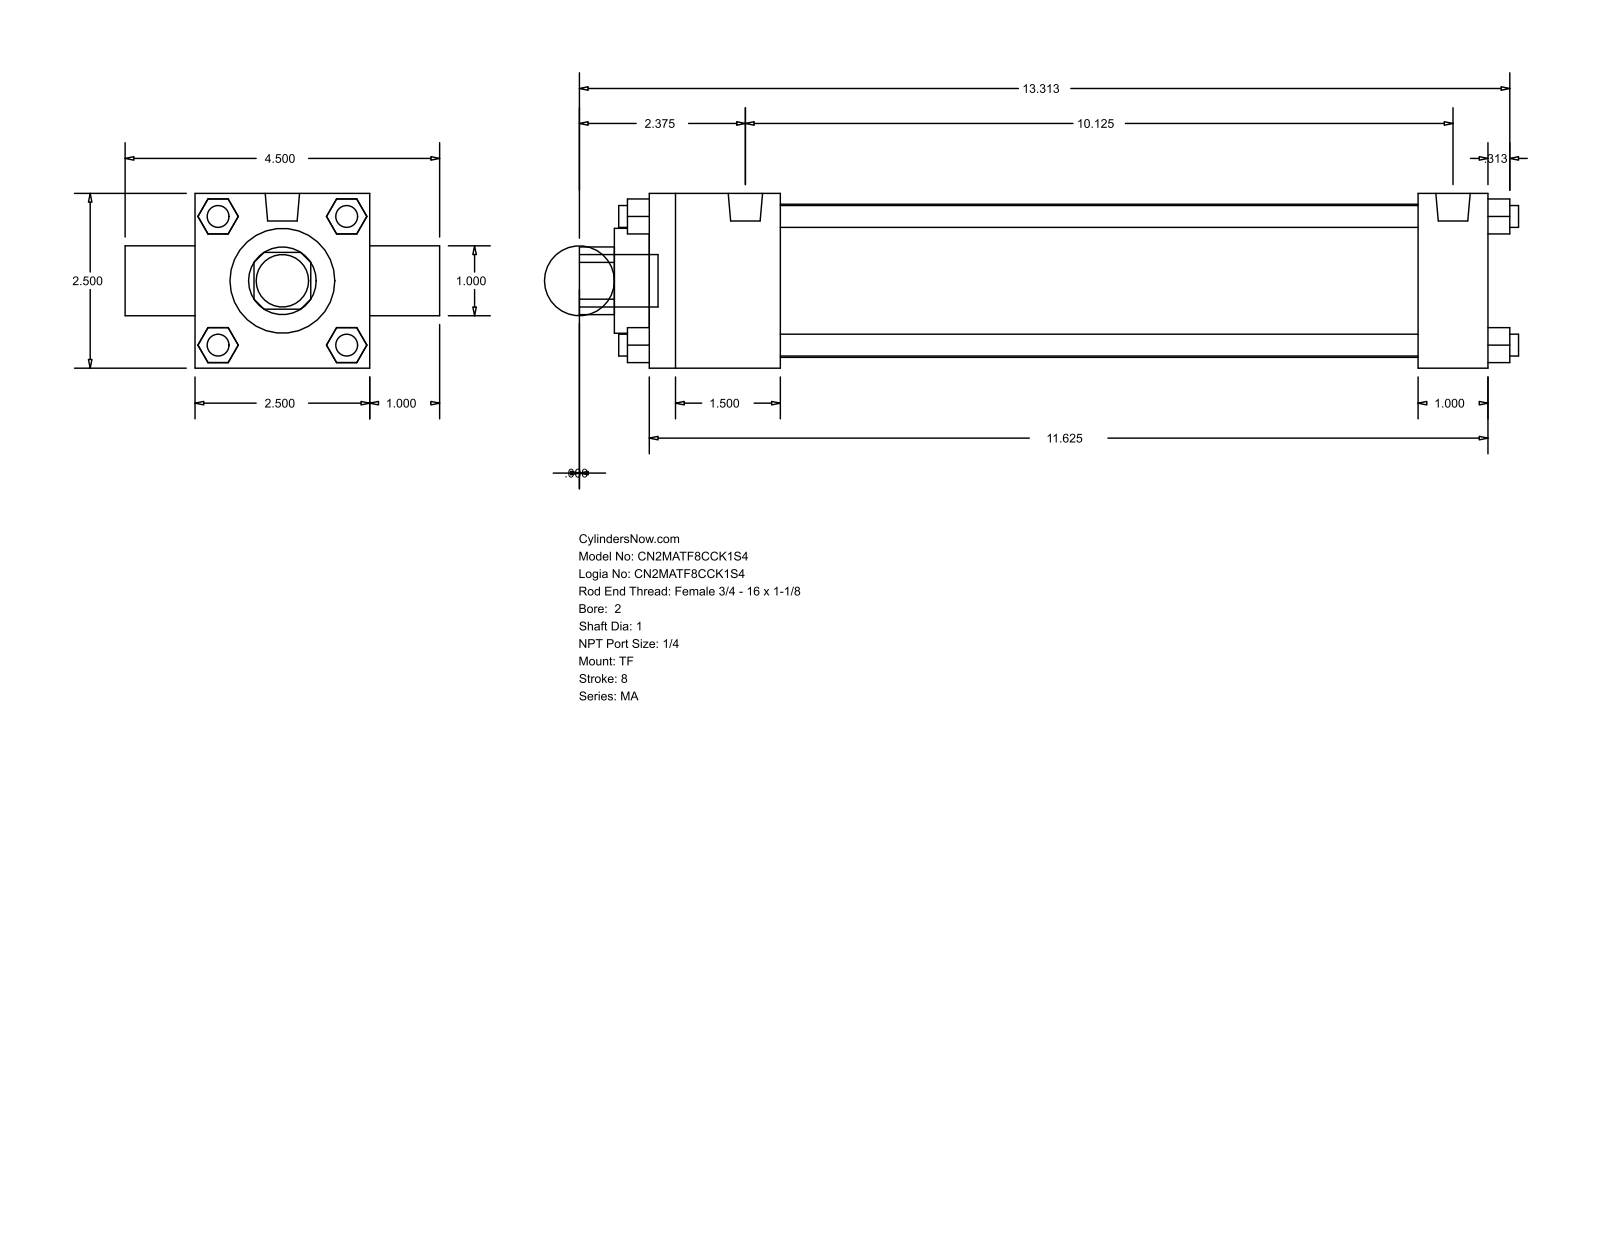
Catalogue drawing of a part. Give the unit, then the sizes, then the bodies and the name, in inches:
Units: inches
Overall size (bounding box): 13.437 × 4.5 × 2.5
Round holes (diameter × count): ⌀1 ×2, ⌀1.5 ×1, ⌀2.19 ×1
Round bosses / shafts (diameter × count): ⌀0.313 ×7, ⌀0.492 ×2, ⌀0.75 ×1
Partial cylindrical surfaces — rounded edges, fillets, slot ends (radius × count): R0.484 ×1
Main face-to-face distances: 2.5, 1, 12, 0.5, 1.875, 11, 9.125, 10.125, 3.5, 1.593
Bodies: 0 solids, 120 faces (92 planar, 28 cylindrical, 0 other)
Part name (STEP PRODUCT): MA_TF__0200_1
STEP written by: GSSL Pune (CONFIG_CONTROL_DESIGN)
